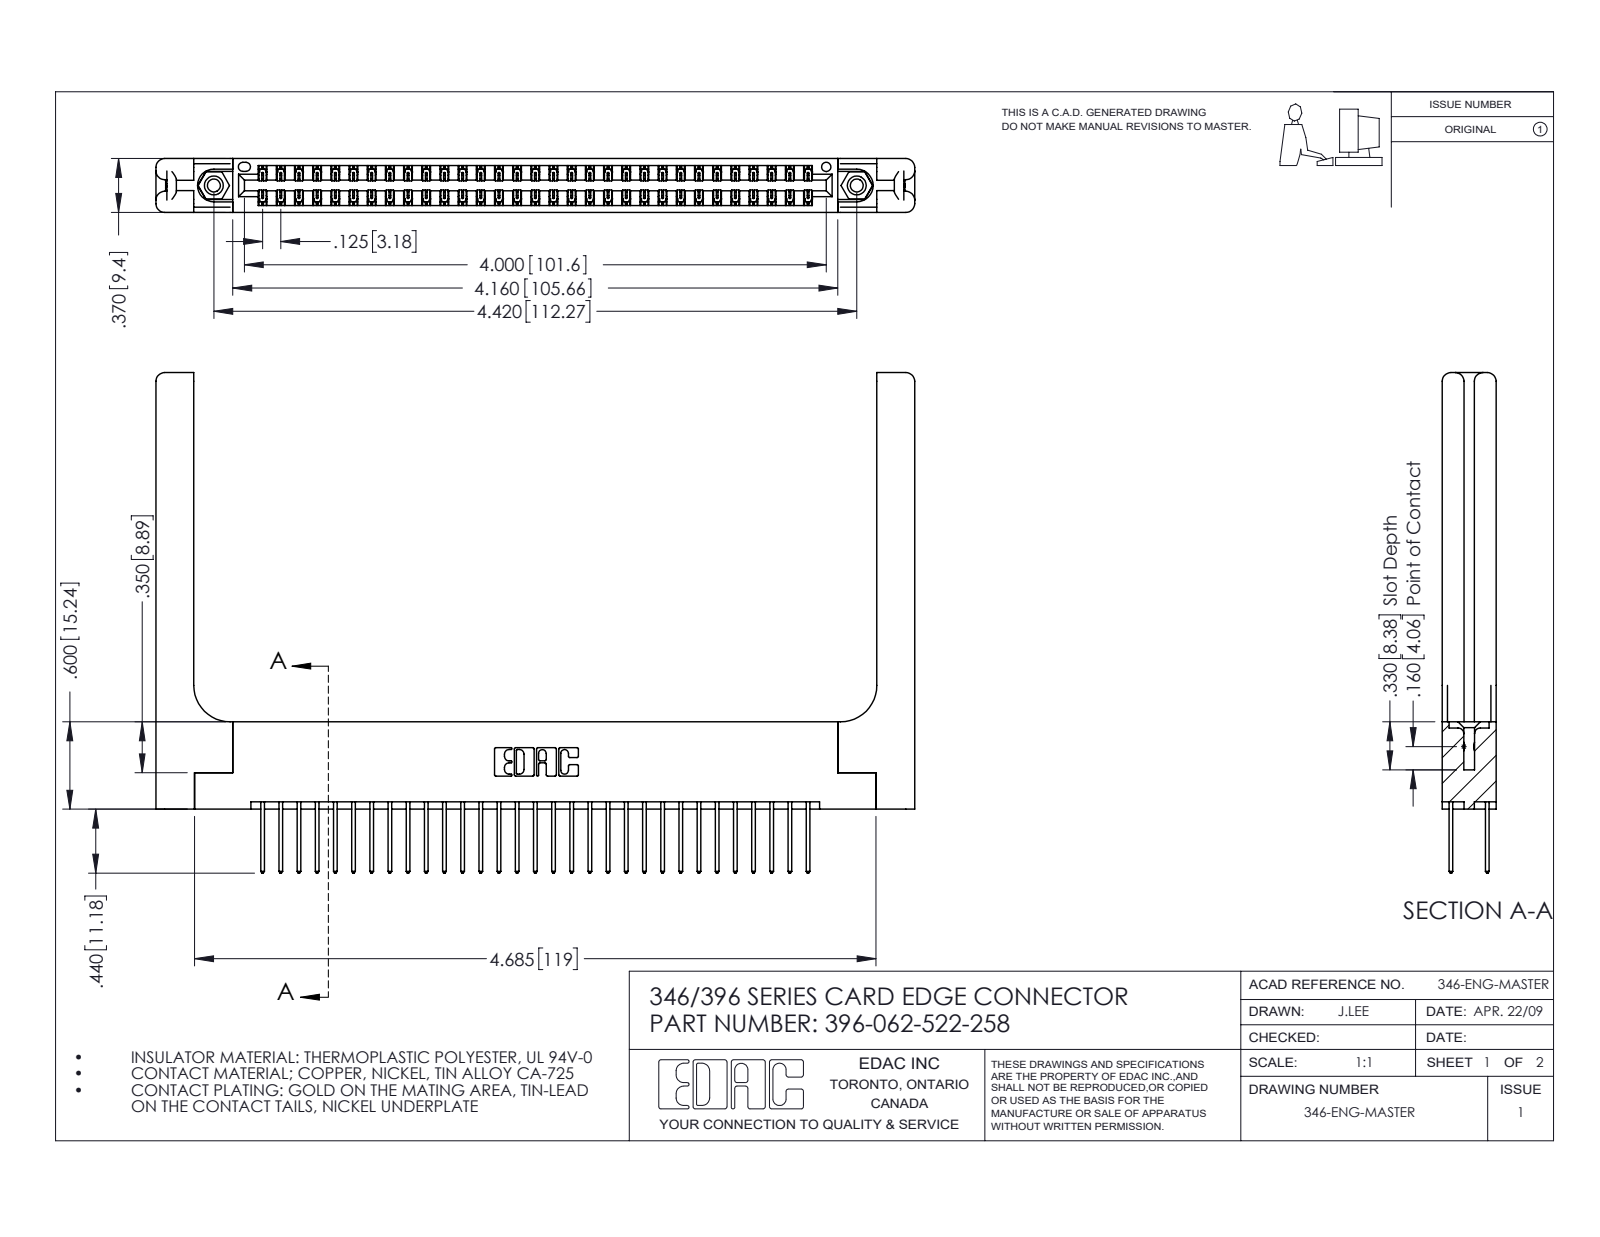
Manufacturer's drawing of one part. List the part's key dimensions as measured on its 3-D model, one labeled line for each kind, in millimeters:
Part name (STEP PRODUCT): 396-062-522-258; 346-220-058_345-220-058; 345-250-001_345-250-001-102; 346 Part_Flush Mounting Lugs - 0.156 Dia-TH (+1 more)
STEP written by: SolidWorks 2016 (CONFIG_CONTROL_DESIGN)
Units: millimetres
Bodies: 67 solids, 3602 faces (2394 planar, 1148 cylindrical, 60 other)
Overall size (bounding box): 132.5 × 87.4 × 9.4
Volume: 20 480 mm³ · Surface area: 23 390 mm²
Round holes (diameter × count): ⌀2.3 ×2, ⌀3.2 ×2, ⌀4 ×2, ⌀1.6 ×1
Round bosses / shafts (diameter × count): ⌀3.9 ×2
Partial cylindrical surfaces — rounded edges, fillets, slot ends (radius × count): R0.2 ×93, R0.3 ×62, R0.3 ×22, R1.5 ×16, R0.2 ×6, R0.8 ×6, R0.7 ×3, R0.4 ×2
Main face-to-face distances: 1.2, 8.2, 9.4, 1.8, 6.4, 3.8, 3.8, 0.6, 7.6, 7
Hole centre spacings: 6.2, 107, 112.3
